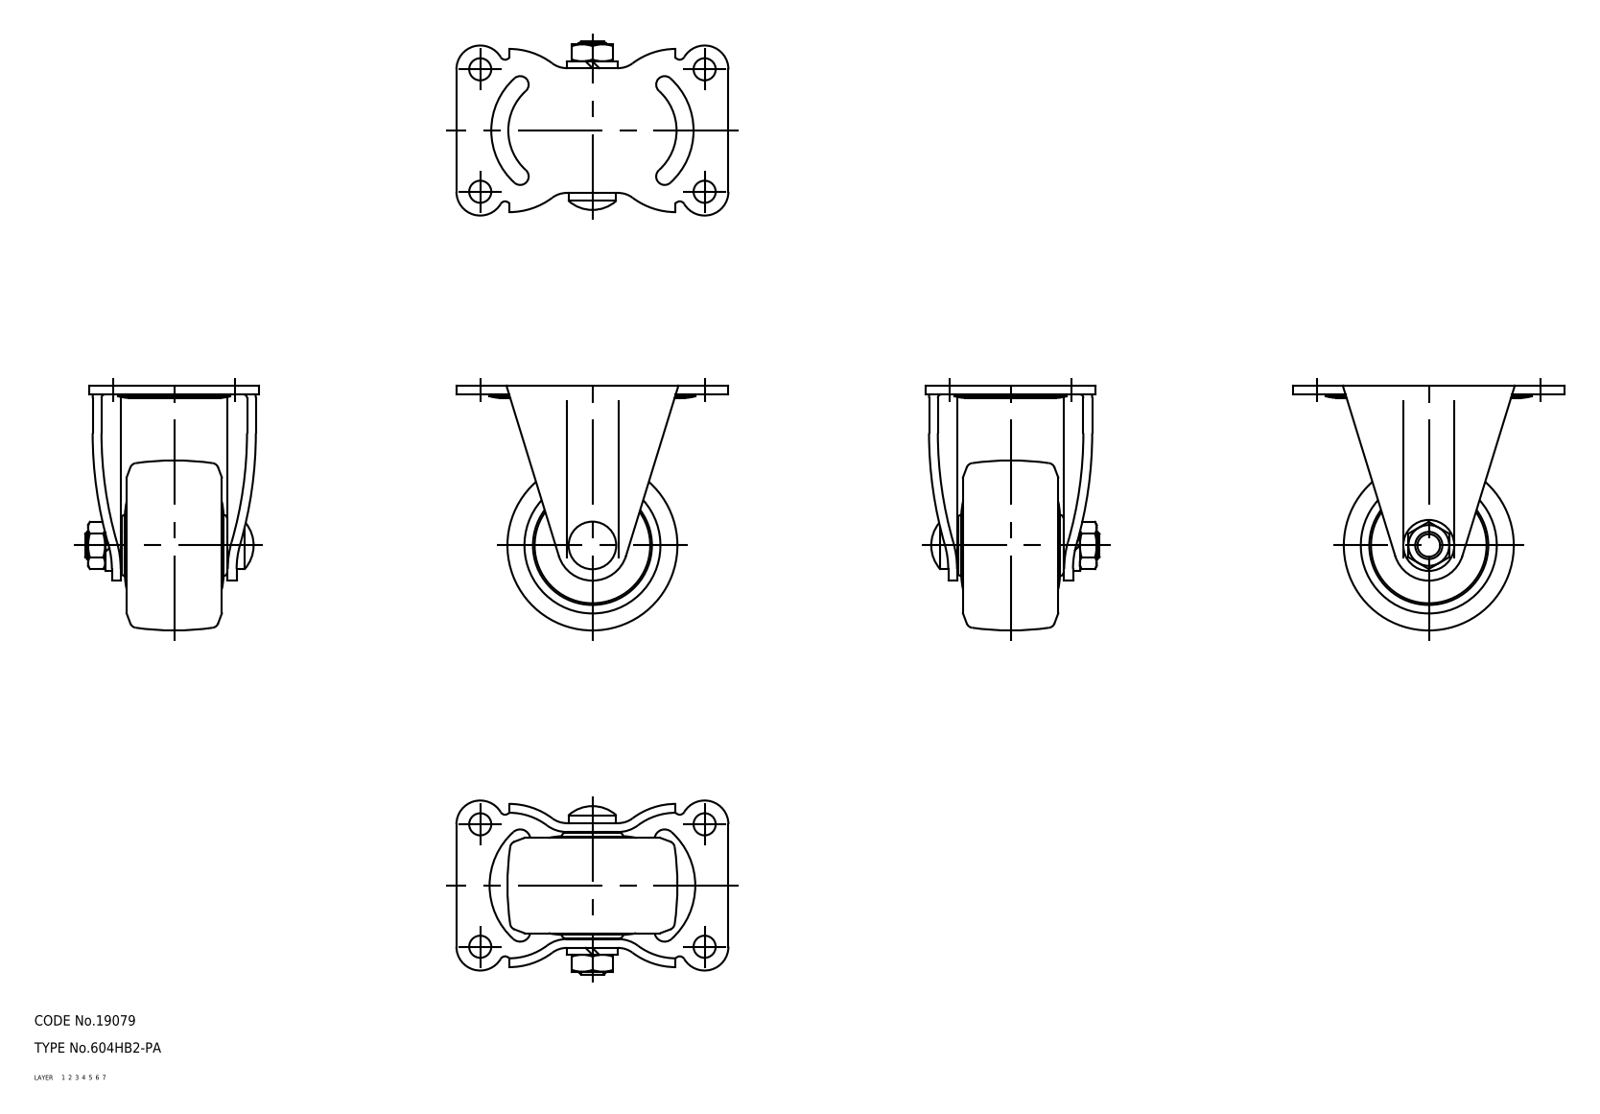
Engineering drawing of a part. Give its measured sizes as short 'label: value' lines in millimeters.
name: wheel; axle; No_604HB2_PA_6288_36
written by: CADfix (AUTOMOTIVE_DESIGN)
unit: mm
bodies: 3 solids, 176 faces (0 planar, 0 cylindrical, 176 other)
size: 80 × 72 × 51.15
volume: 71 854 mm³; area: 26 373 mm²
